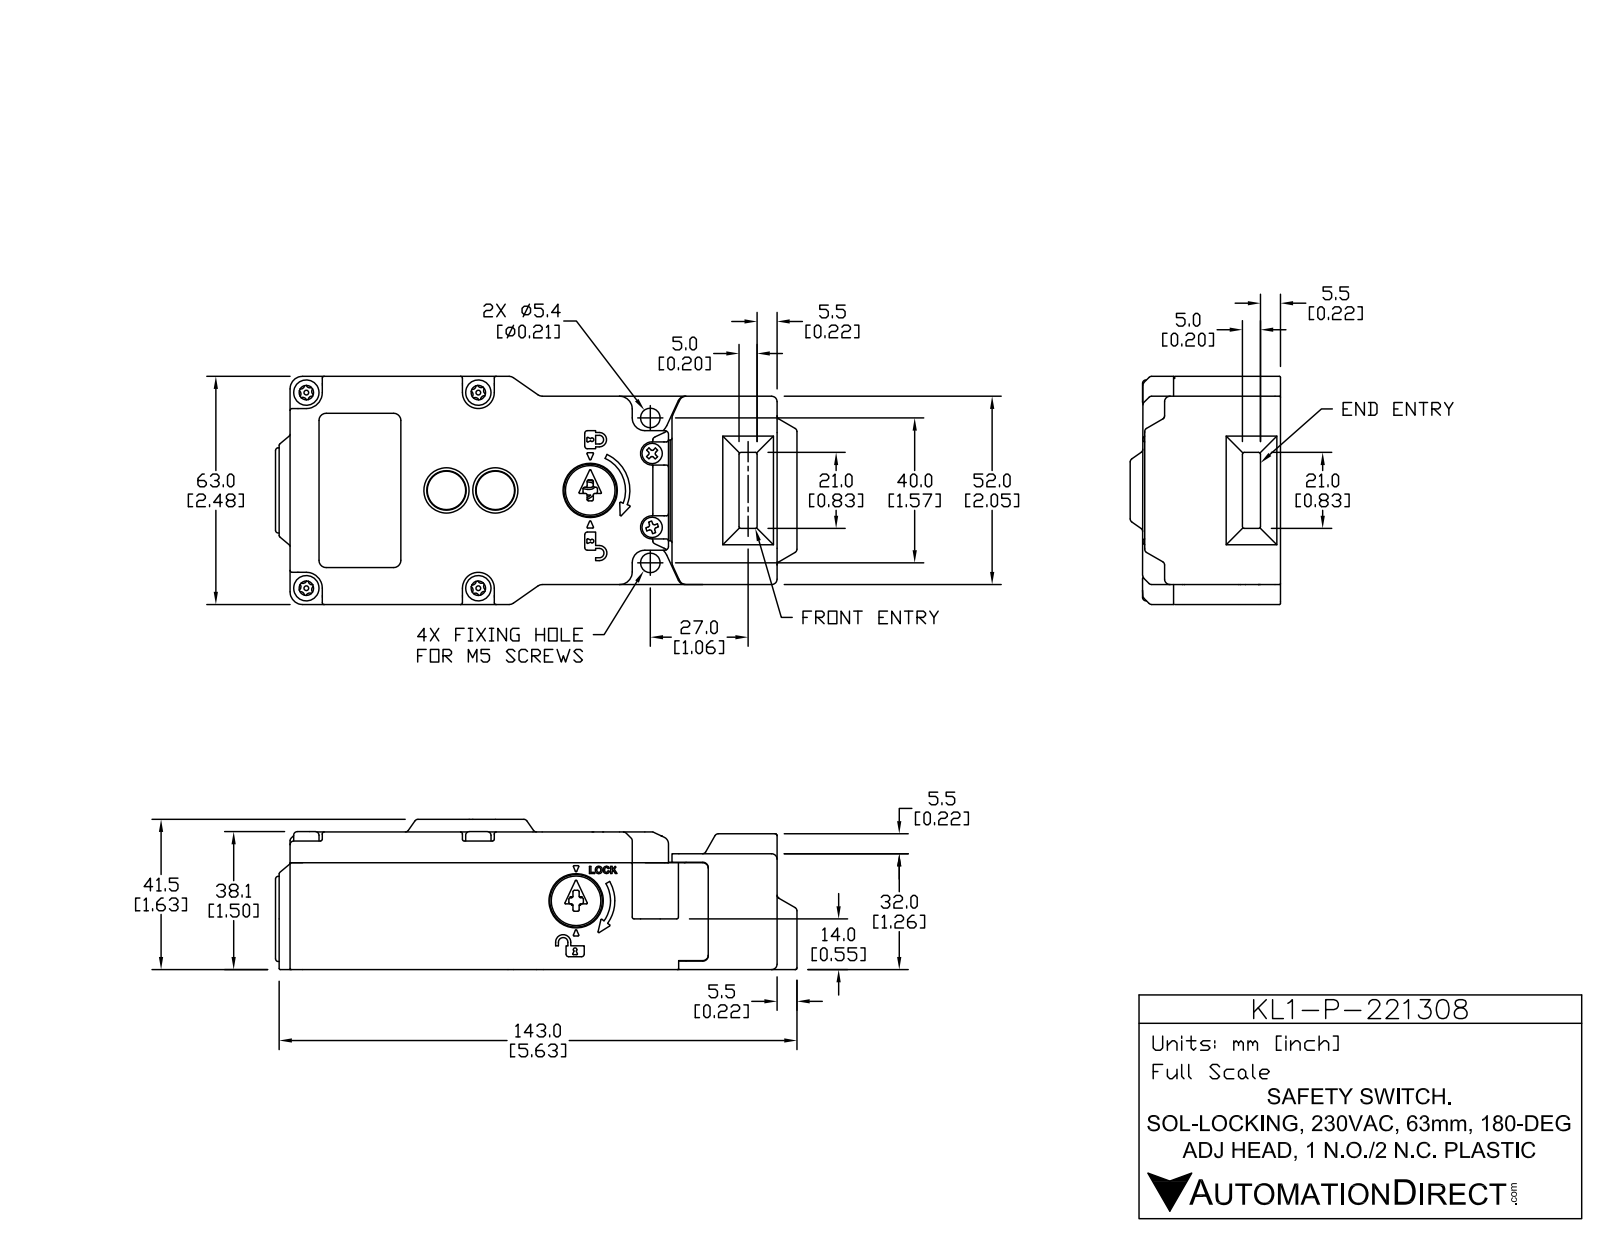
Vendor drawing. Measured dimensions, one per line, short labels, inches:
name: KL1-P-221308
written by: SolidWorks 2017 (AUTOMOTIVE_DESIGN)
unit: in
bodies: 18 solids, 3047 faces (909 planar, 1225 cylindrical, 913 other)
size: 5.669 × 2.48 × 1.634
volume: 6.348 in³; area: 118.8 in²
holes: 4× ⌀0.102, 4× ⌀0.134, 4× ⌀0.157, 4× ⌀0.161, 4× ⌀0.177, 4× ⌀0.197, 2× ⌀0.079, 2× ⌀0.083, 2× ⌀0.118, 2× ⌀0.126, 2× ⌀0.142, 2× ⌀0.264
bosses: 4× ⌀0.276, 4× ⌀0.138, 4× ⌀0.051, 3× ⌀0.197, 3× ⌀0.039, 2× ⌀0.571, 2× ⌀0.417, 2× ⌀0.362
rounds: 348× R0.02, 126× R0.012, 106× R0.039, 30× R0.008, 24× R0.016, 16× R0.059, 14× R0.006, 12× R0.028
face distances: 0.098, 0.118, 0.217, 1.496, 1.398, 1.402, 1.303, 0.094, 2.264, 2.146
hole spacings: 0.404, 0.498, 0.515, 0.549, 0.784, 0.803, 1.079, 1.118
